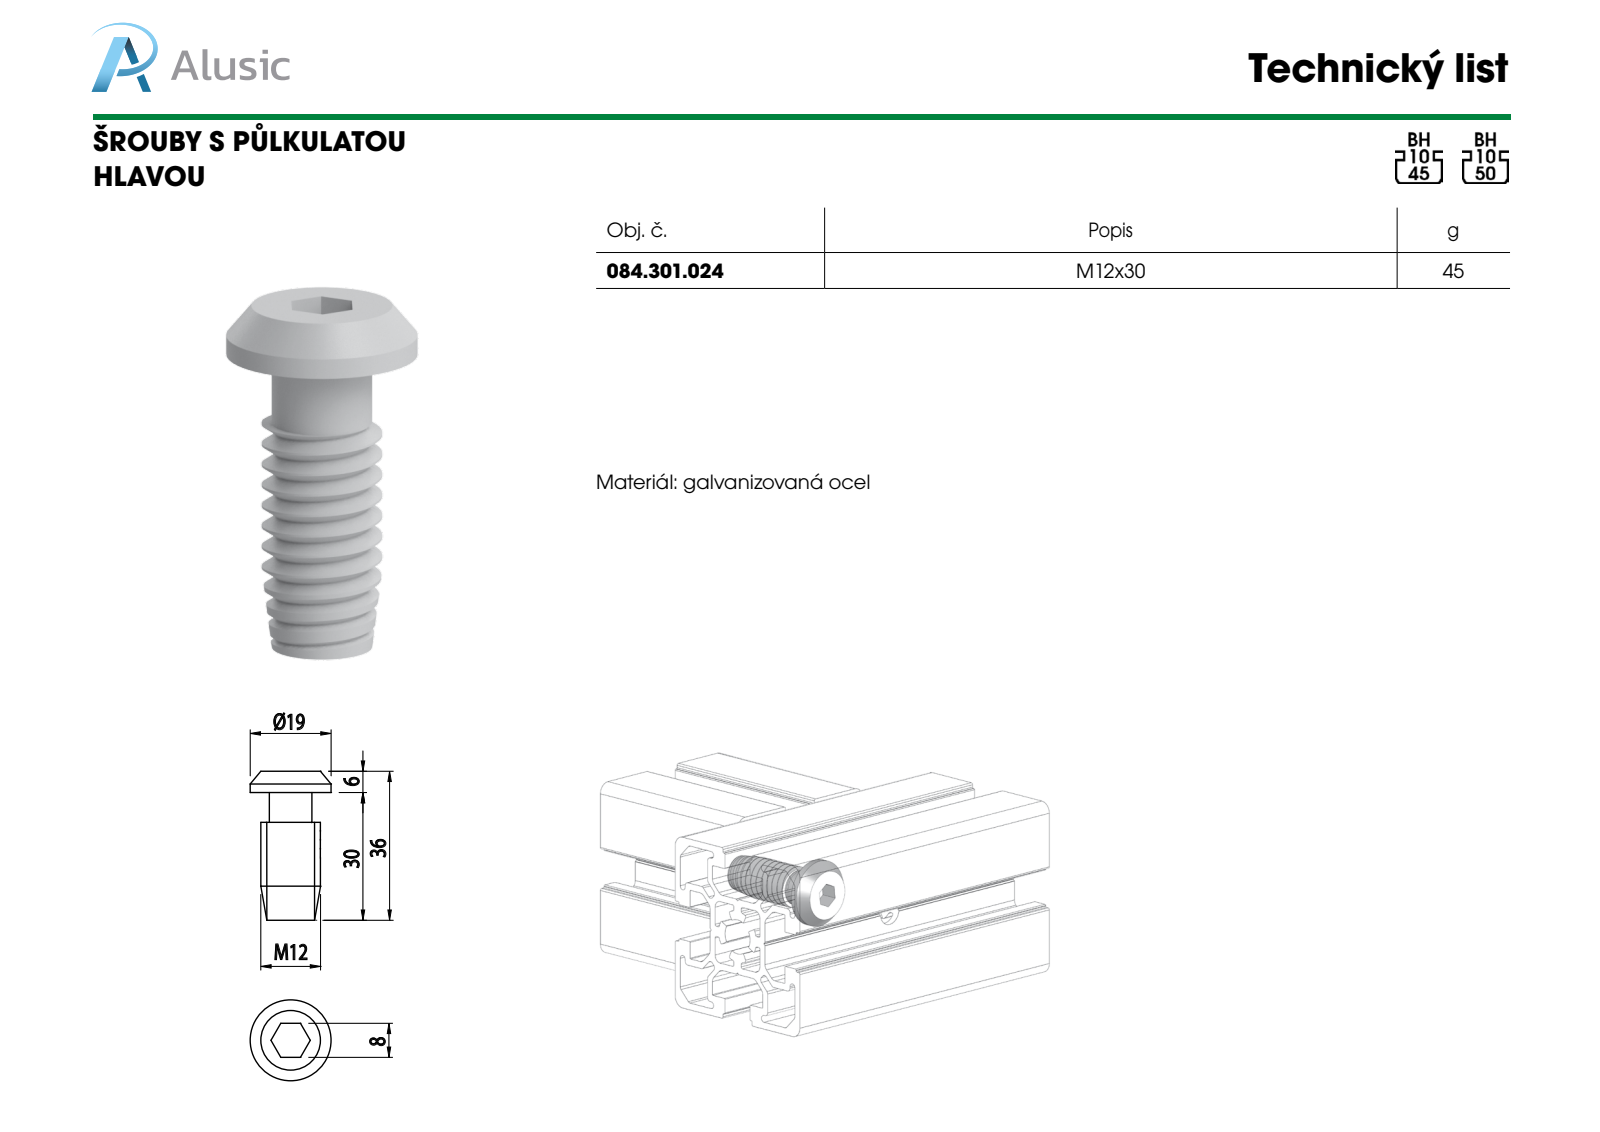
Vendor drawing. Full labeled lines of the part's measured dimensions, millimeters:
Part name (STEP PRODUCT): 084.301.024
STEP written by: SolidWorks 2011 (CONFIG_CONTROL_DESIGN)
Units: millimetres
Bodies: 1 solid, 47 faces (13 planar, 19 cylindrical, 15 other)
Overall size (bounding box): 35 × 19 × 19
Volume: 3 662 mm³ · Surface area: 2 345 mm²
Round bosses / shafts (diameter × count): ⌀19 ×1, ⌀12 ×1, ⌀10 ×1
Main face-to-face distances: 5, 30, 35, 6, 23, 7, 12
